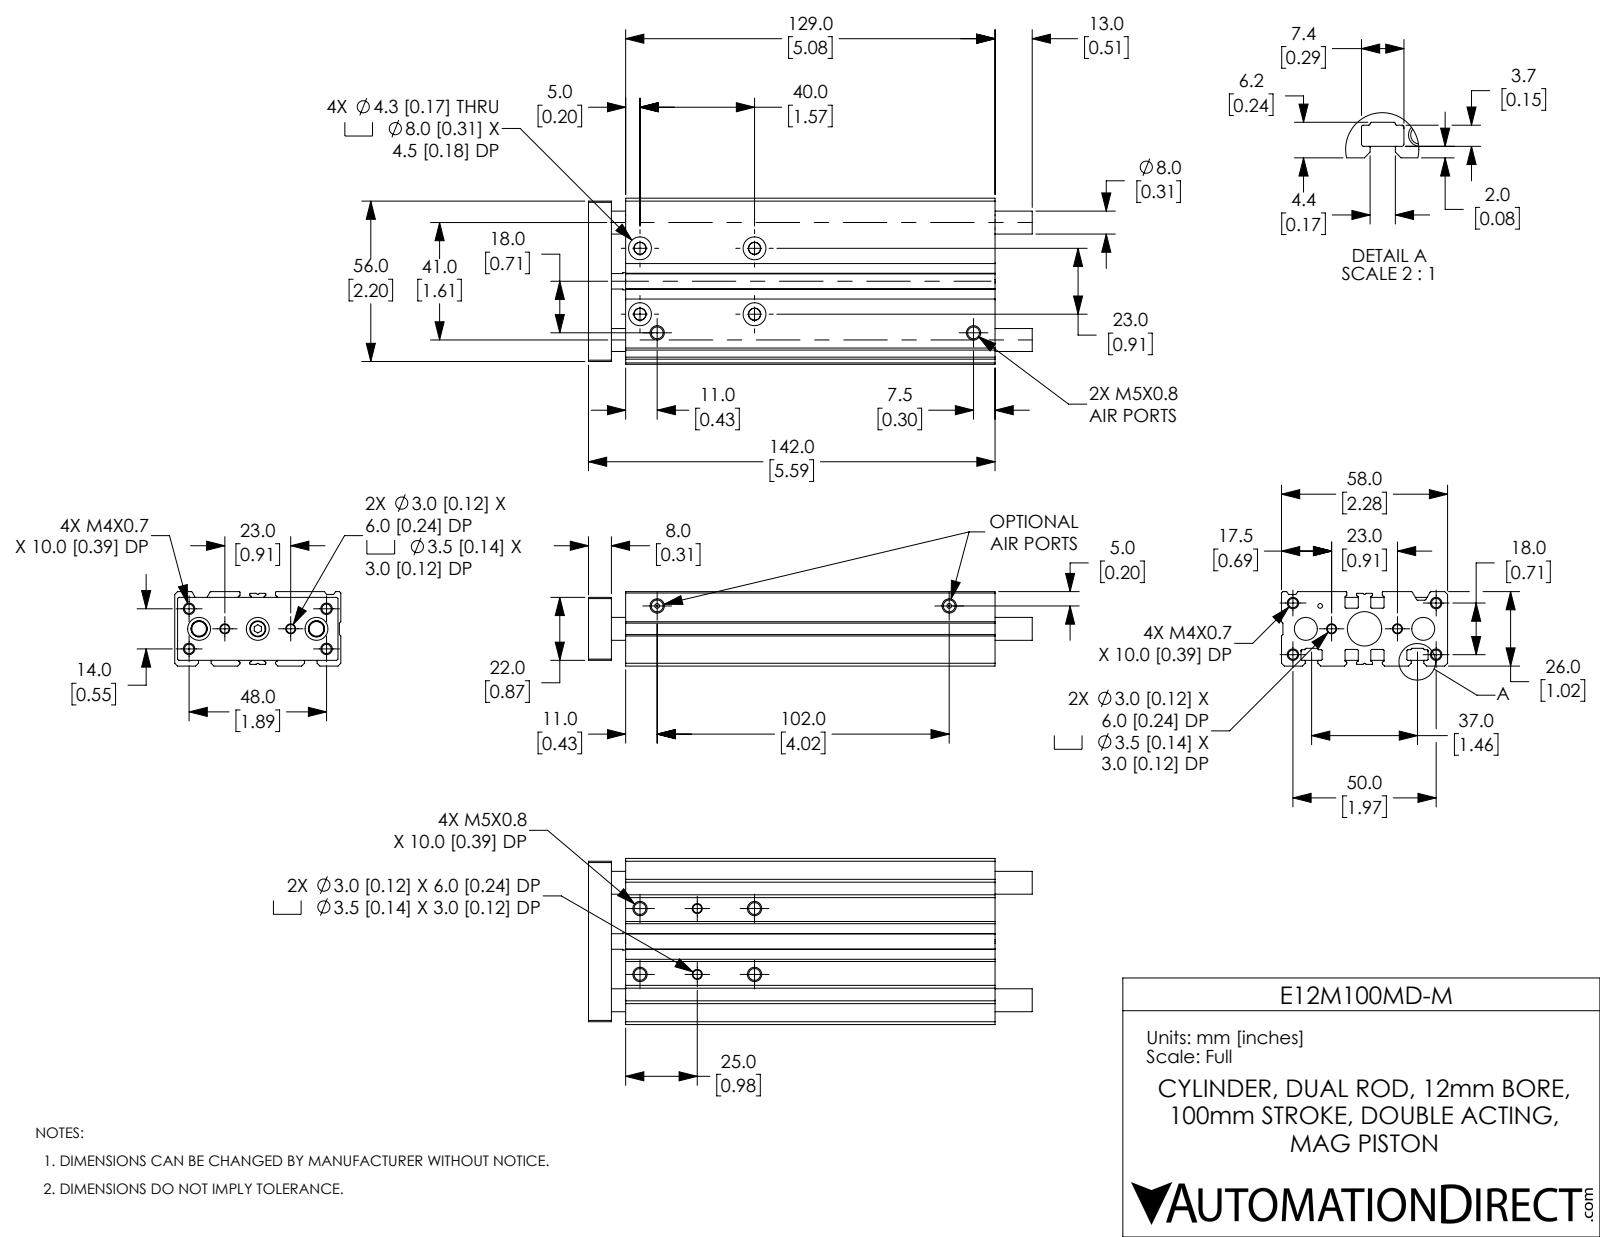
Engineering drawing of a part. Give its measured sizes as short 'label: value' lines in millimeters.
name: E12M100MD-M_ENDPLATE; E12M100MD-D_BODY; E12M100MD-M
written by: SolidWorks 2019 (CONFIG_CONTROL_DESIGN)
unit: mm
bodies: 5 solids, 414 faces (137 planar, 188 cylindrical, 89 other)
size: 155 × 58 × 26
volume: 167 154 mm³; area: 64 348 mm²
holes: 8× ⌀3.24, 8× ⌀4.13, 7× ⌀8, 4× ⌀3, 4× ⌀3.5, 4× ⌀4.3, 3× ⌀1.67, 3× ⌀4, 2× ⌀5.59, 1× ⌀8, 1× ⌀12, 1× ⌀12
bosses: 1× ⌀6, 1× ⌀5.59
rounds: 20× R0.4, 18× R0.2, 8× R0.25, 6× R0.3, 4× R0.5
face distances: 26, 58, 5.8, 9, 20.2, 26.8, 31.2, 22.2, 35.8, 4.6
hole spacings: 2.24, 7.83, 10.06, 14.33, 16.03, 16.22, 20, 23
